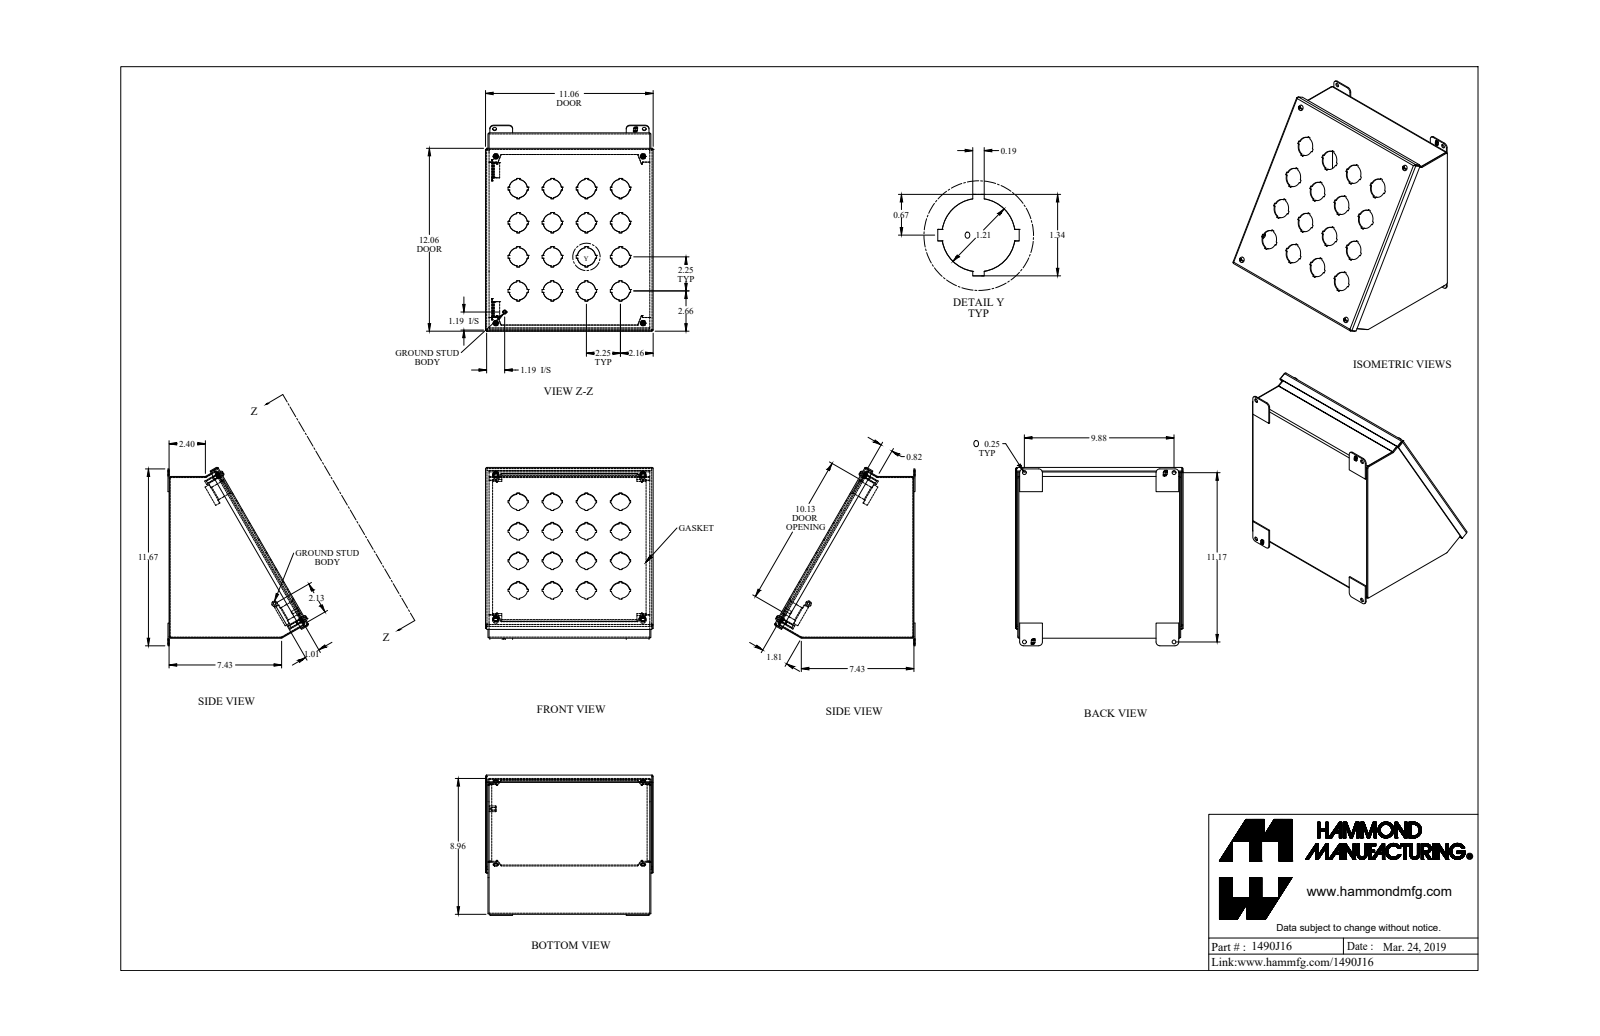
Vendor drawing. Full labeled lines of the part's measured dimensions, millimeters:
Part name (STEP PRODUCT): 1490J16_Default
STEP written by: SolidWorks 2019 (CONFIG_CONTROL_DESIGN)
Units: millimetres
Bodies: 25 solids, 966 faces (691 planar, 235 cylindrical, 40 other)
Overall size (bounding box): 298.9 × 281 × 235.2
Volume: 702 200 mm³ · Surface area: 745 200 mm²
Round holes (diameter × count): ⌀30.7 ×16, ⌀6.4 ×8, ⌀4 ×4, ⌀10.3 ×4, ⌀4 ×1
Round bosses / shafts (diameter × count): ⌀9.9 ×4, ⌀7 ×4, ⌀4.8 ×4, ⌀3.8 ×4, ⌀9.5 ×1, ⌀6.4 ×1, ⌀4.8 ×1
Partial cylindrical surfaces — rounded edges, fillets, slot ends (radius × count): R2.7 ×18, R0.9 ×12, R0.7 ×8, R2.2 ×8, R6.4 ×8, R3.2 ×4, R4.1 ×4, R4.3 ×4
Main face-to-face distances: 1.8, 269.4, 271.2, 1.8, 271.2, 273.1, 269.1, 267.3, 270.9, 6.4
Hole centre spacings: 127.8, 57.2, 80.8, 114.3, 246.6, 279.4, 372.7, 161.6
